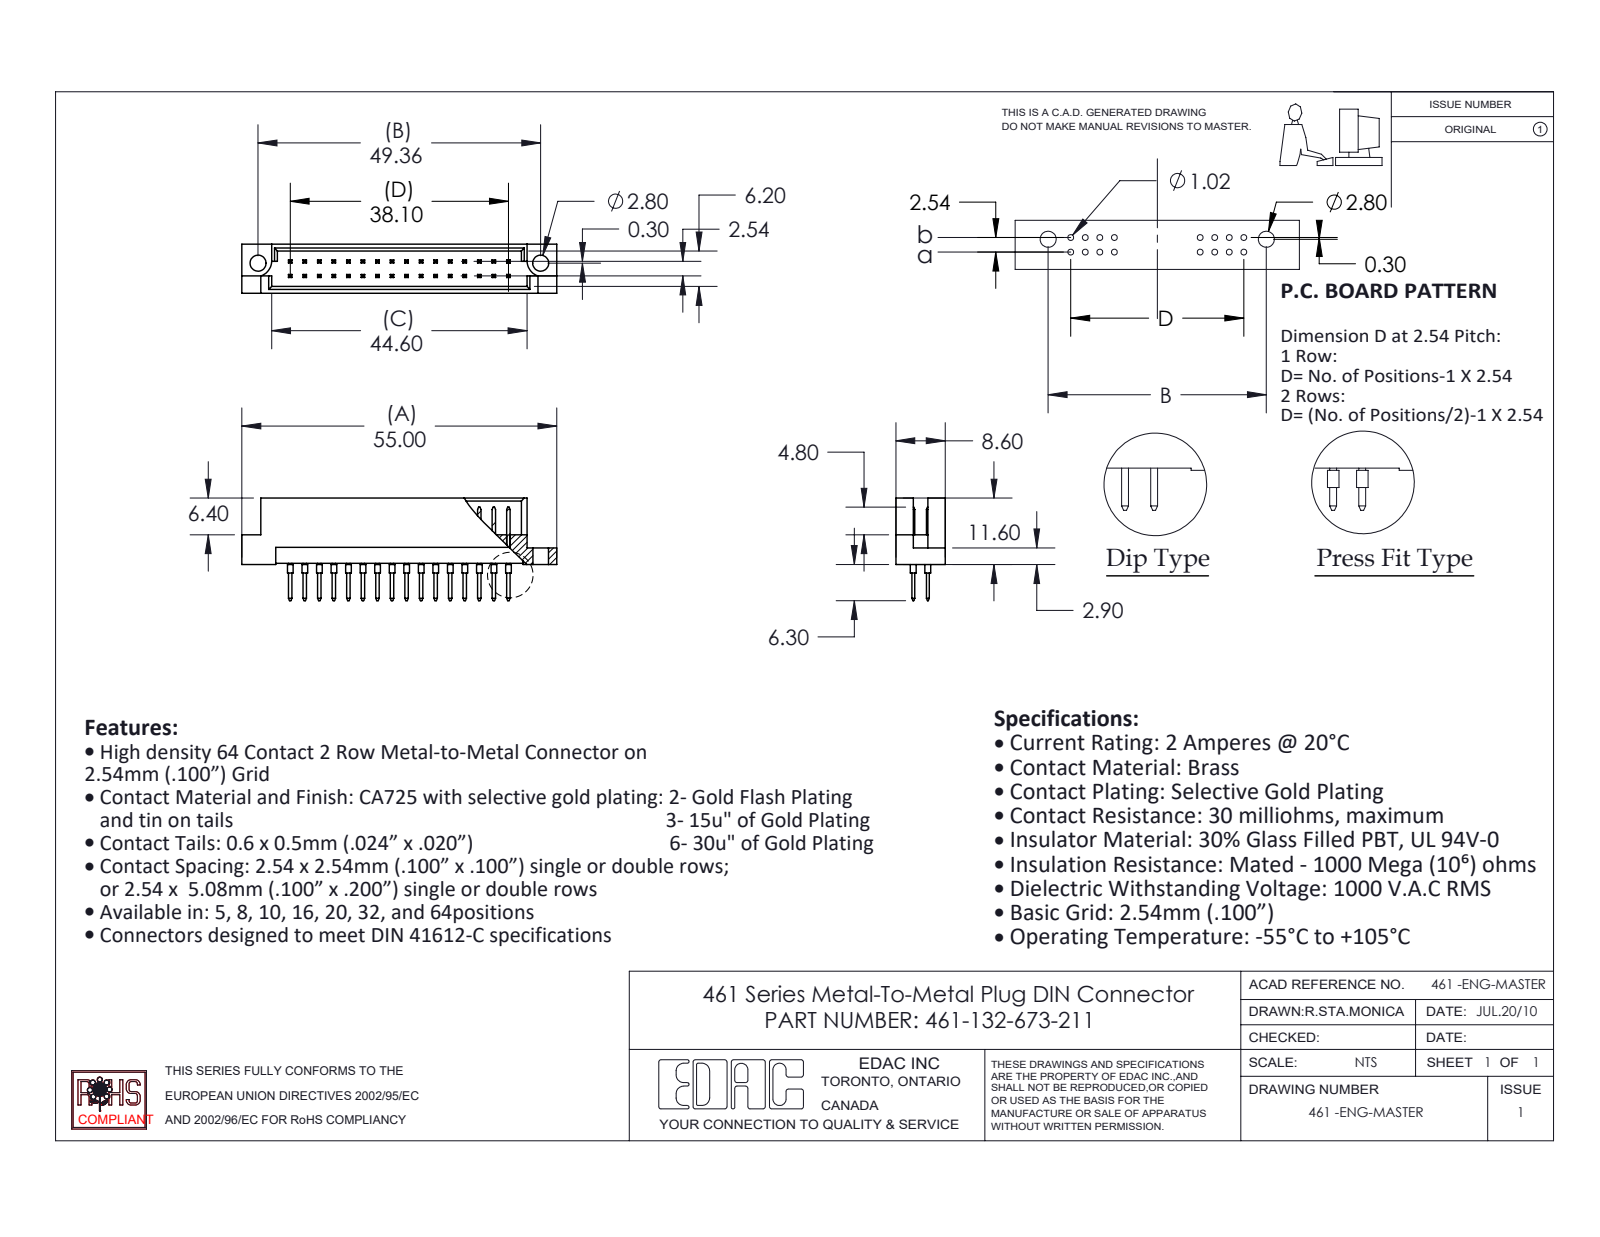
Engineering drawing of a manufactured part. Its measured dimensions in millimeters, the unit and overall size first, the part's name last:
Units: millimetres
Overall size (bounding box): 55 × 17.9 × 8.6
Round holes (diameter × count): ⌀2.8 ×2
Round bosses / shafts (diameter × count): ⌀1 ×32
Partial cylindrical surfaces — rounded edges, fillets, slot ends (radius × count): R2.8 ×2
Main face-to-face distances: 1.2, 7.4, 2.54, 8.6, 6.2, 2.78, 5.82, 1.58, 4.62, 3.28
Hole centre spacings: 49.36
Volume: 2 830 mm³ · Surface area: 4 459 mm²
Bodies: 33 solids, 880 faces (810 planar, 70 cylindrical, 0 other)
Part name (STEP PRODUCT): 461 Part_32; 461-132-673-211; 461-290_73
STEP written by: SolidWorks 2020 (CONFIG_CONTROL_DESIGN)
